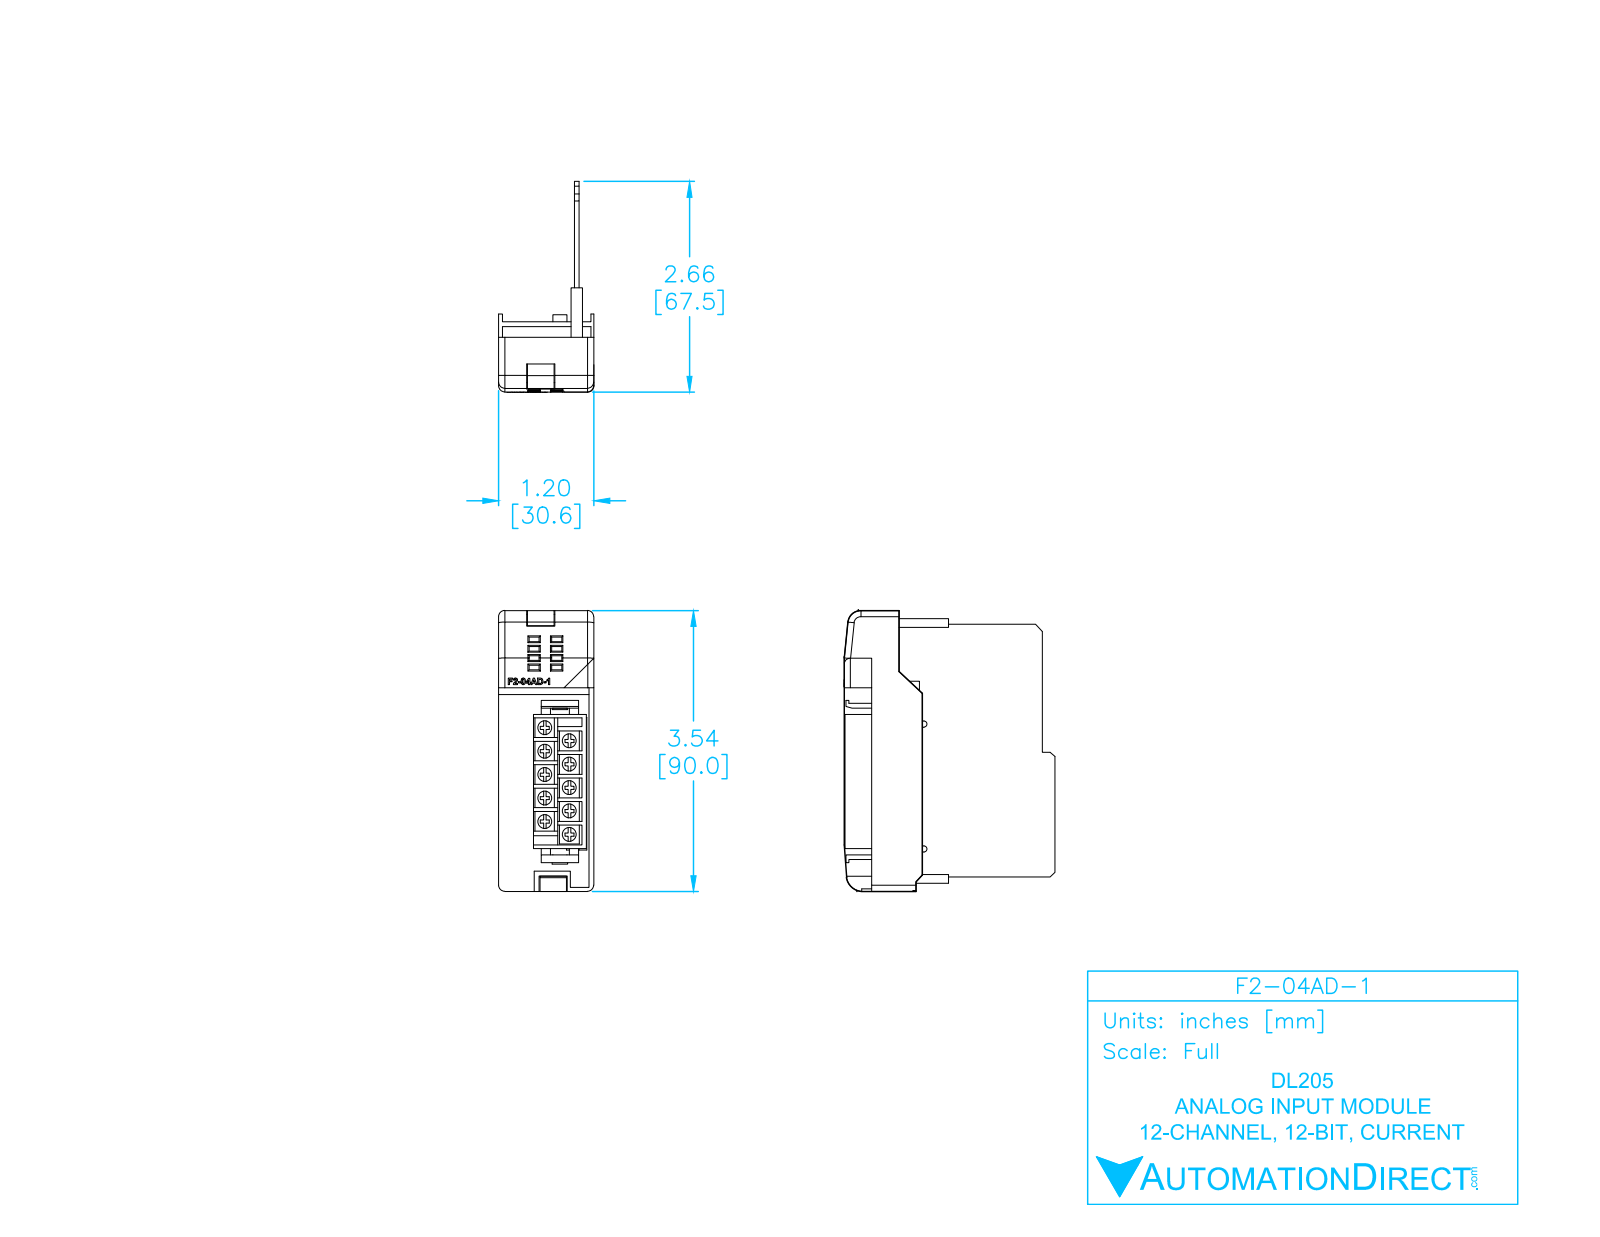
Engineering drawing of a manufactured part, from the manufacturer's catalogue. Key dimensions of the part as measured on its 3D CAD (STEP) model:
Part name (STEP PRODUCT): F2-04AD-1_ModuleCase_light_NEW
STEP written by: SolidWorks 2009 (AUTOMOTIVE_DESIGN)
Units: millimetres
Bodies: 6 solids, 576 faces (425 planar, 75 cylindrical, 76 other)
Overall size (bounding box): 90 × 67.61 × 30.55
Volume: 25 374 mm³ · Surface area: 28 532 mm²
Round bosses / shafts (diameter × count): ⌀4.5 ×10
Partial cylindrical surfaces — rounded edges, fillets, slot ends (radius × count): R0.35 ×16, R2 ×9, R0.25 ×2, R1 ×2, R1.25 ×2, R4.12 ×1, R5.39 ×1
Main face-to-face distances: 1.5, 4.72, 6.22, 2.37, 3.87, 2.35, 3.22, 0.85, 7.25, 8.14
